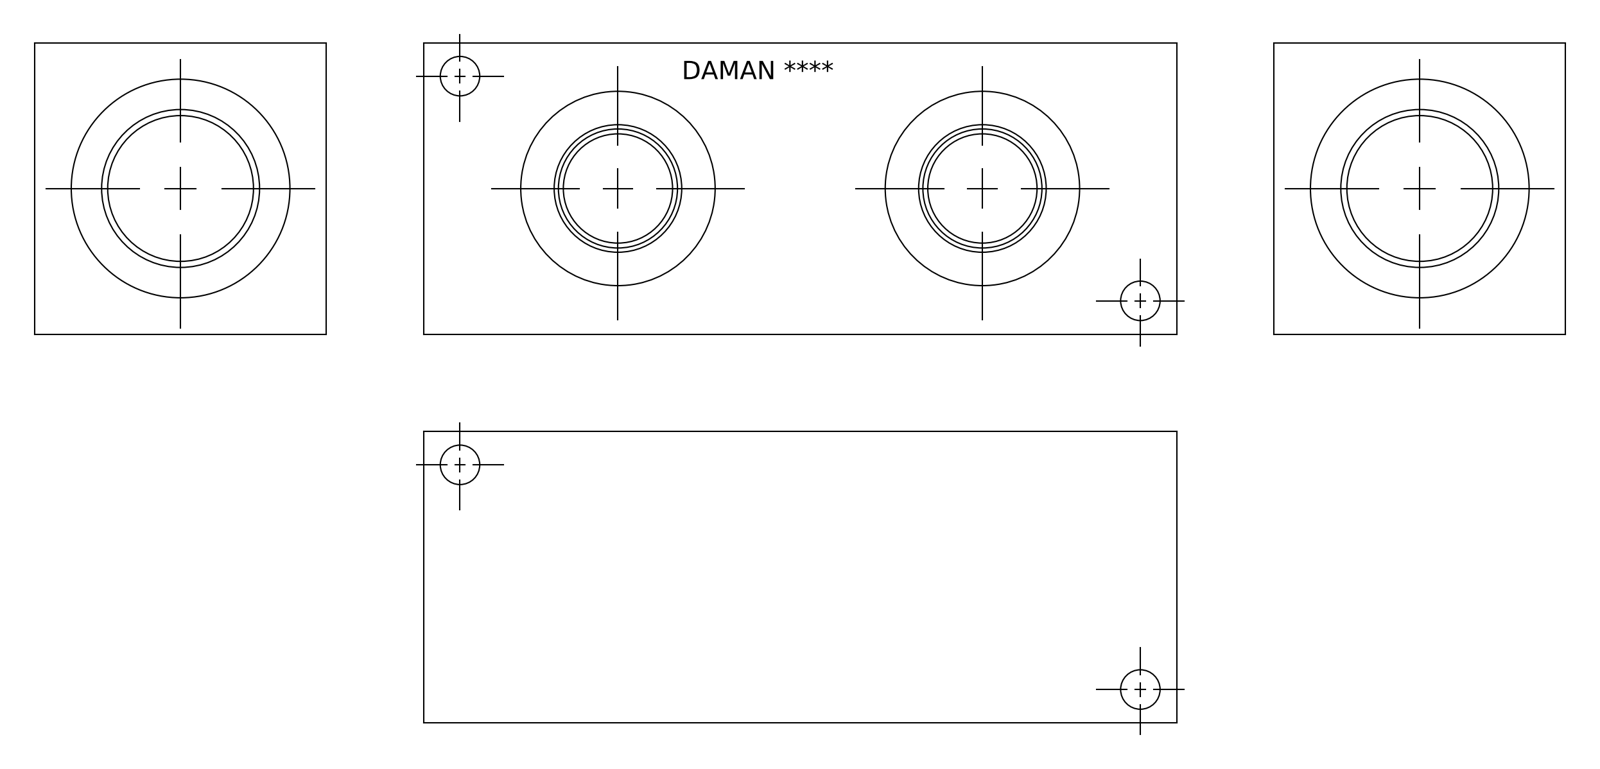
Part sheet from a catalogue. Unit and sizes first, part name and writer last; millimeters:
Units: millimetres
Overall size (bounding box): 196.85 × 76.2 × 76.2
Round holes (diameter × count): ⌀10.31 ×4, ⌀28.57 ×2, ⌀31.27 ×2, ⌀33.76 ×2, ⌀49.12 ×2, ⌀33.34 ×1, ⌀33.35 ×1, ⌀35.51 ×1, ⌀38.1 ×1, ⌀39.22 ×1, ⌀41.27 ×1, ⌀41.28 ×1
Main face-to-face distances: 76.2, 0.79, 196.85, 196.06, 75.41, 195.27, 19.84, 19.05, 177.01, 176.22
Hole centre spacings: 50.65, 139.64, 187.24, 95.25
Volume: 959 103 mm³ · Surface area: 95 049 mm²
Bodies: 1 solid, 368 faces (216 planar, 29 cylindrical, 123 other)
Part name (STEP PRODUCT): Part_+H0000216S_3D
STEP written by: Autodesk Inventor 2020 (AUTOMOTIVE_DESIGN)
